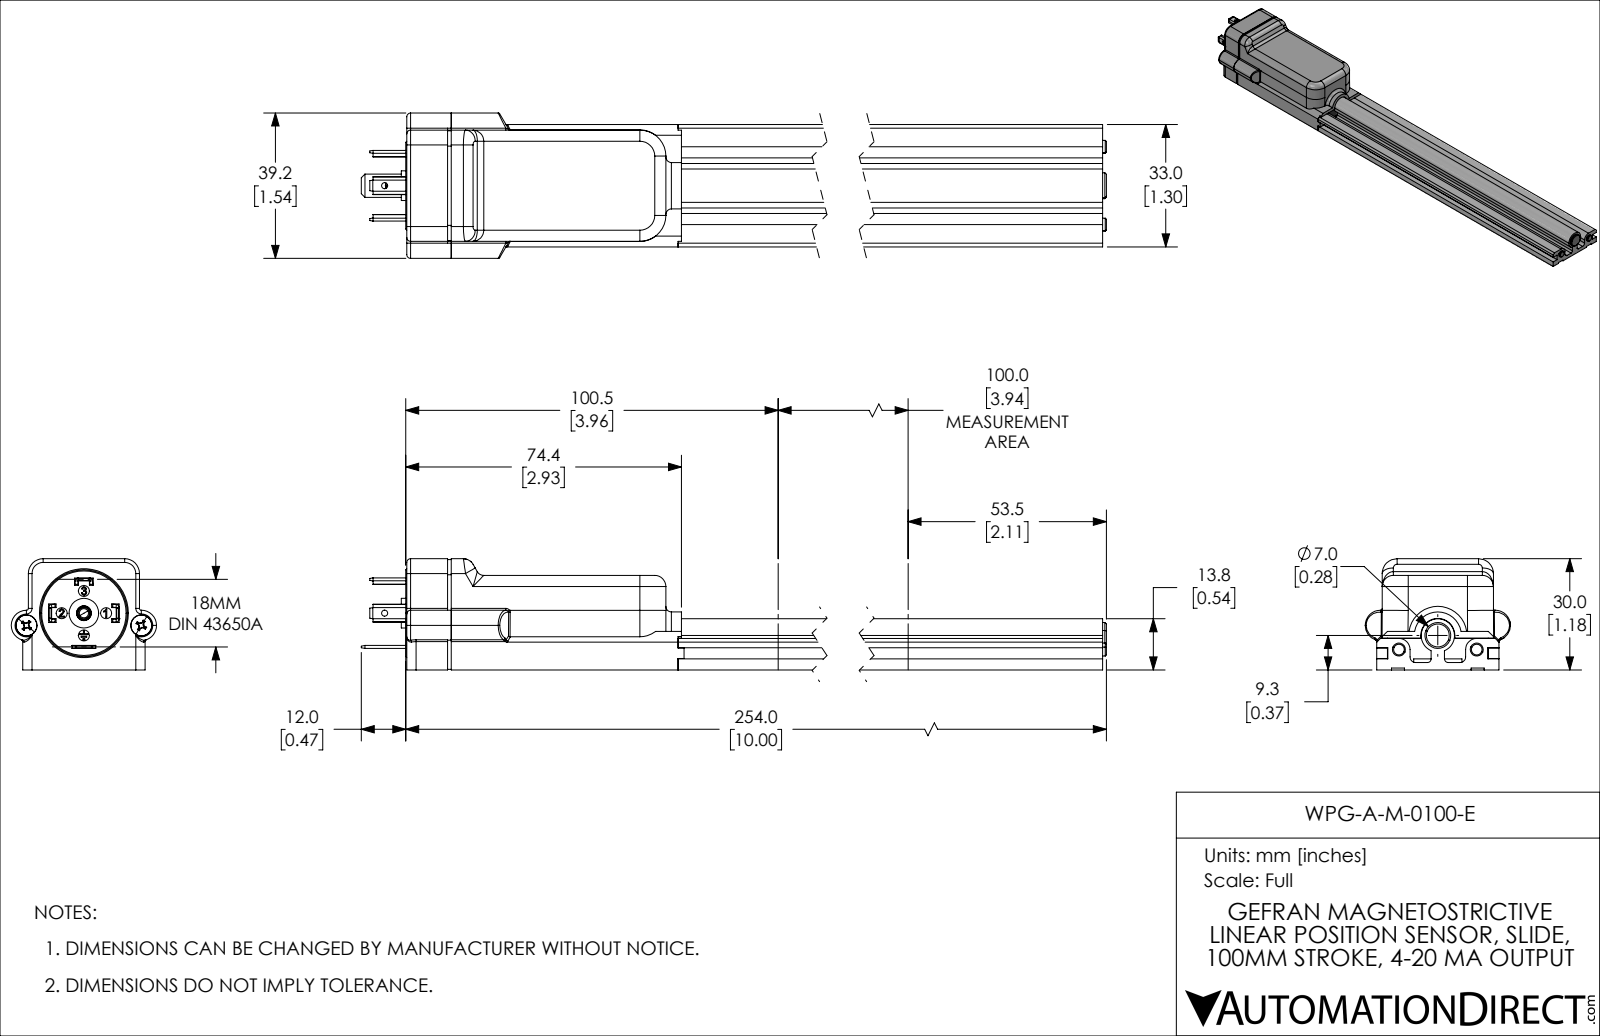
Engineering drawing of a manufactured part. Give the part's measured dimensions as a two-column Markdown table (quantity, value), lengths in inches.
| quantity | value |
| --- | --- |
| part name | WPG-A-M-0100-E |
| STEP written by | SolidWorks 2021 (CONFIG_CONTROL_DESIGN) |
| units | inches |
| bodies | 15 solids, 589 faces (371 planar, 139 cylindrical, 79 other) |
| overall size | 10.472 × 1.543 × 1.181 |
| volume | 6.208 in³ |
| surface area | 63.42 in² |
| round holes (diameter × count) | 0.118 × 5, 0.059 × 2, 0.065 × 2, 0.126 × 2, 0.224 × 2, 0.063 × 1, 0.098 × 1, 0.157 × 1 |
| round bosses / shafts (diameter × count) | 0.22 × 2, 0.138 × 2, 0.112 × 2, 0.354 × 1, 0.315 × 1, 0.276 × 1, 0.209 × 1, 0.155 × 1 |
| partial cylindrical surfaces (radius × count) | 0.02 × 8, 0.118 × 8, 0.033 × 6, 0.039 × 5, 0.031 × 4, 0.059 × 4, 0.161 × 4, 0.276 × 4 |
| main face-to-face distances | 0.039, 0.118, 0.059, 0.098, 0.217, 0.236, 0.886, 1.181, 0.335, 1.299 |
| hole center spacings | 0.236, 0.334, 0.396, 0.472, 0.484, 0.619, 0.624, 0.712 |
